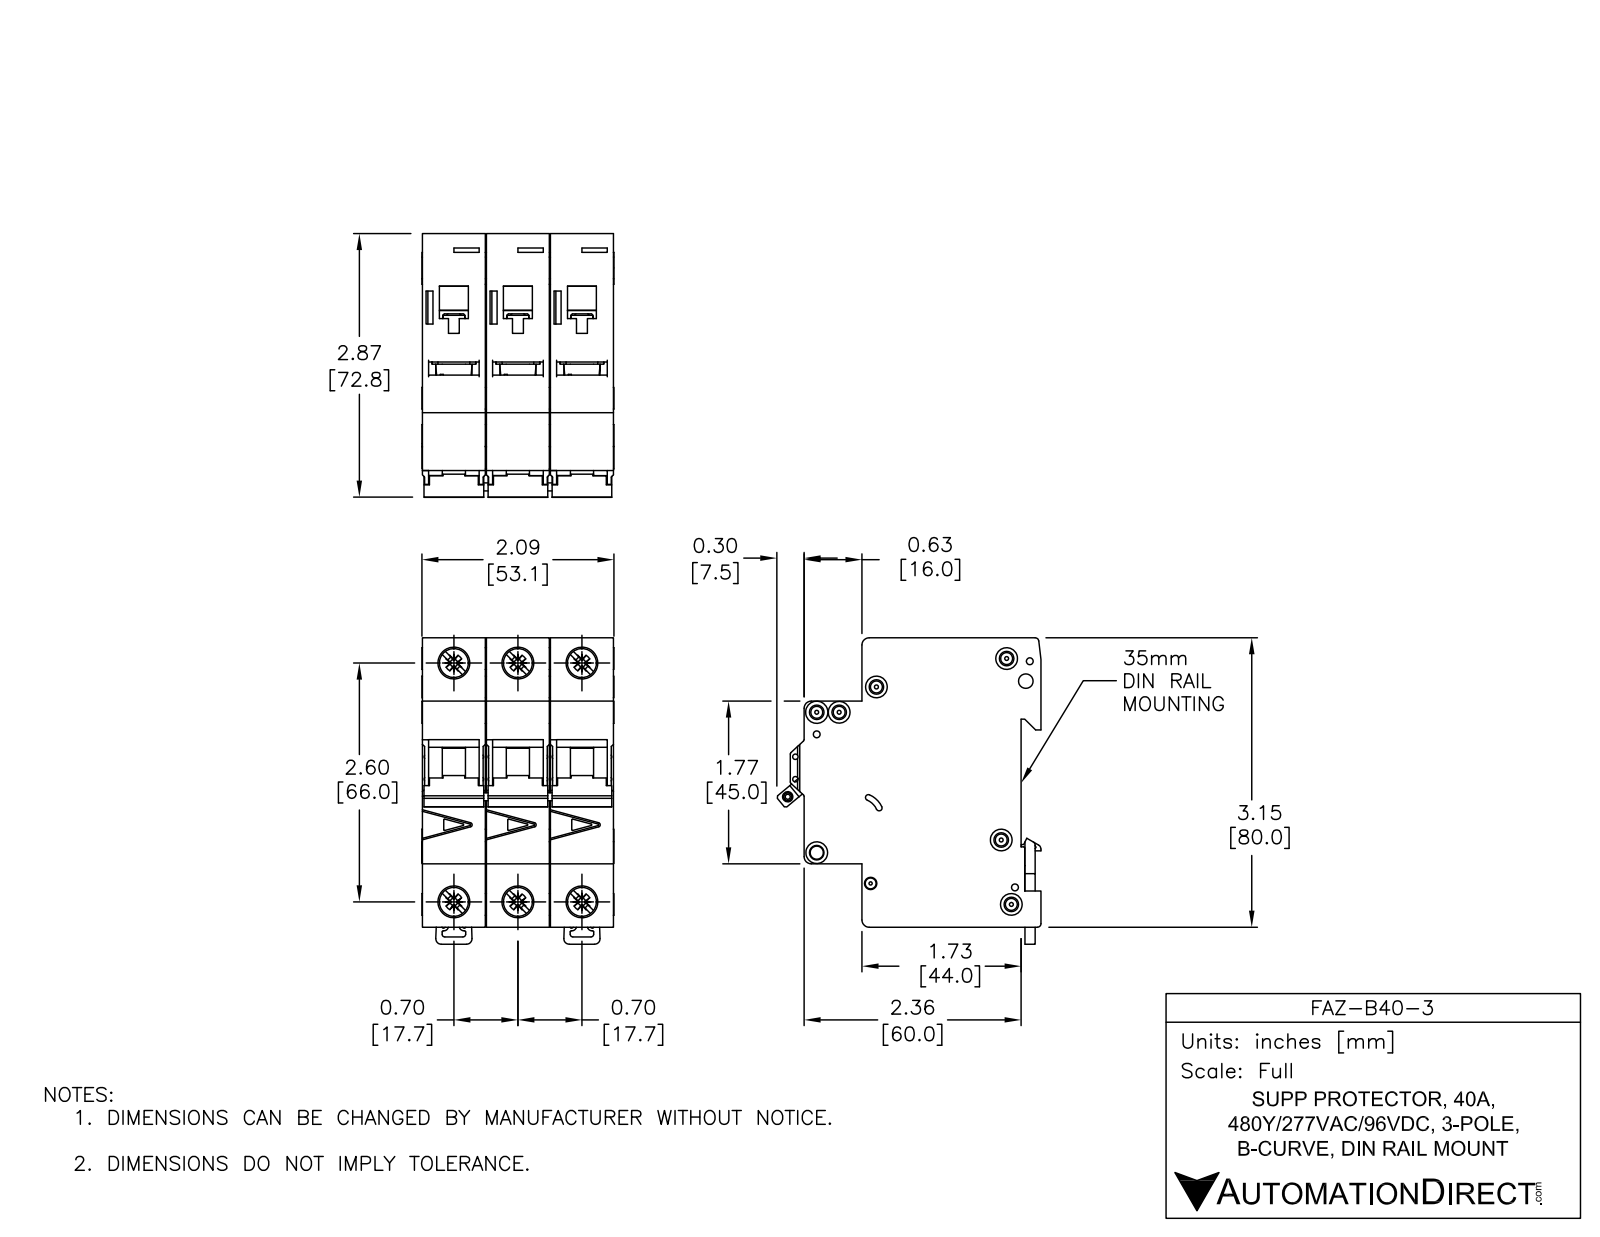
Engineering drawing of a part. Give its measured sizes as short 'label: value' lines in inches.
name: FAZ-B40-3
written by: SolidWorks 2014 (AUTOMOTIVE_DESIGN)
unit: in
bodies: 11 solids, 1650 faces (697 planar, 590 cylindrical, 363 other)
size: 3.338 × 2.876 × 2.091
volume: 13.71 in³; area: 89.98 in²
holes: 6× ⌀0.142, 4× ⌀0.323, 3× ⌀0.075, 2× ⌀0.043, 2× ⌀0.059, 2× ⌀0.157, 2× ⌀0.281, 1× ⌀0.085, 1× ⌀0.087, 1× ⌀0.1, 1× ⌀0.13, 1× ⌀0.134
bosses: 4× ⌀0.236, 3× ⌀0.098, 2× ⌀0.323
rounds: 68× R0.01, 25× R0.02, 12× R0.039, 12× R0.079, 11× R0.008, 3× R0.071, 2× R0.031, 2× R0.118
face distances: 0.697, 0.689, 1.394, 1.386, 2.083, 0.705, 3.129, 0.217, 1.949, 1.732
hole spacings: 0.697, 2.69, 2.598, 0.244, 0.537, 1.394, 2.948, 0.189
